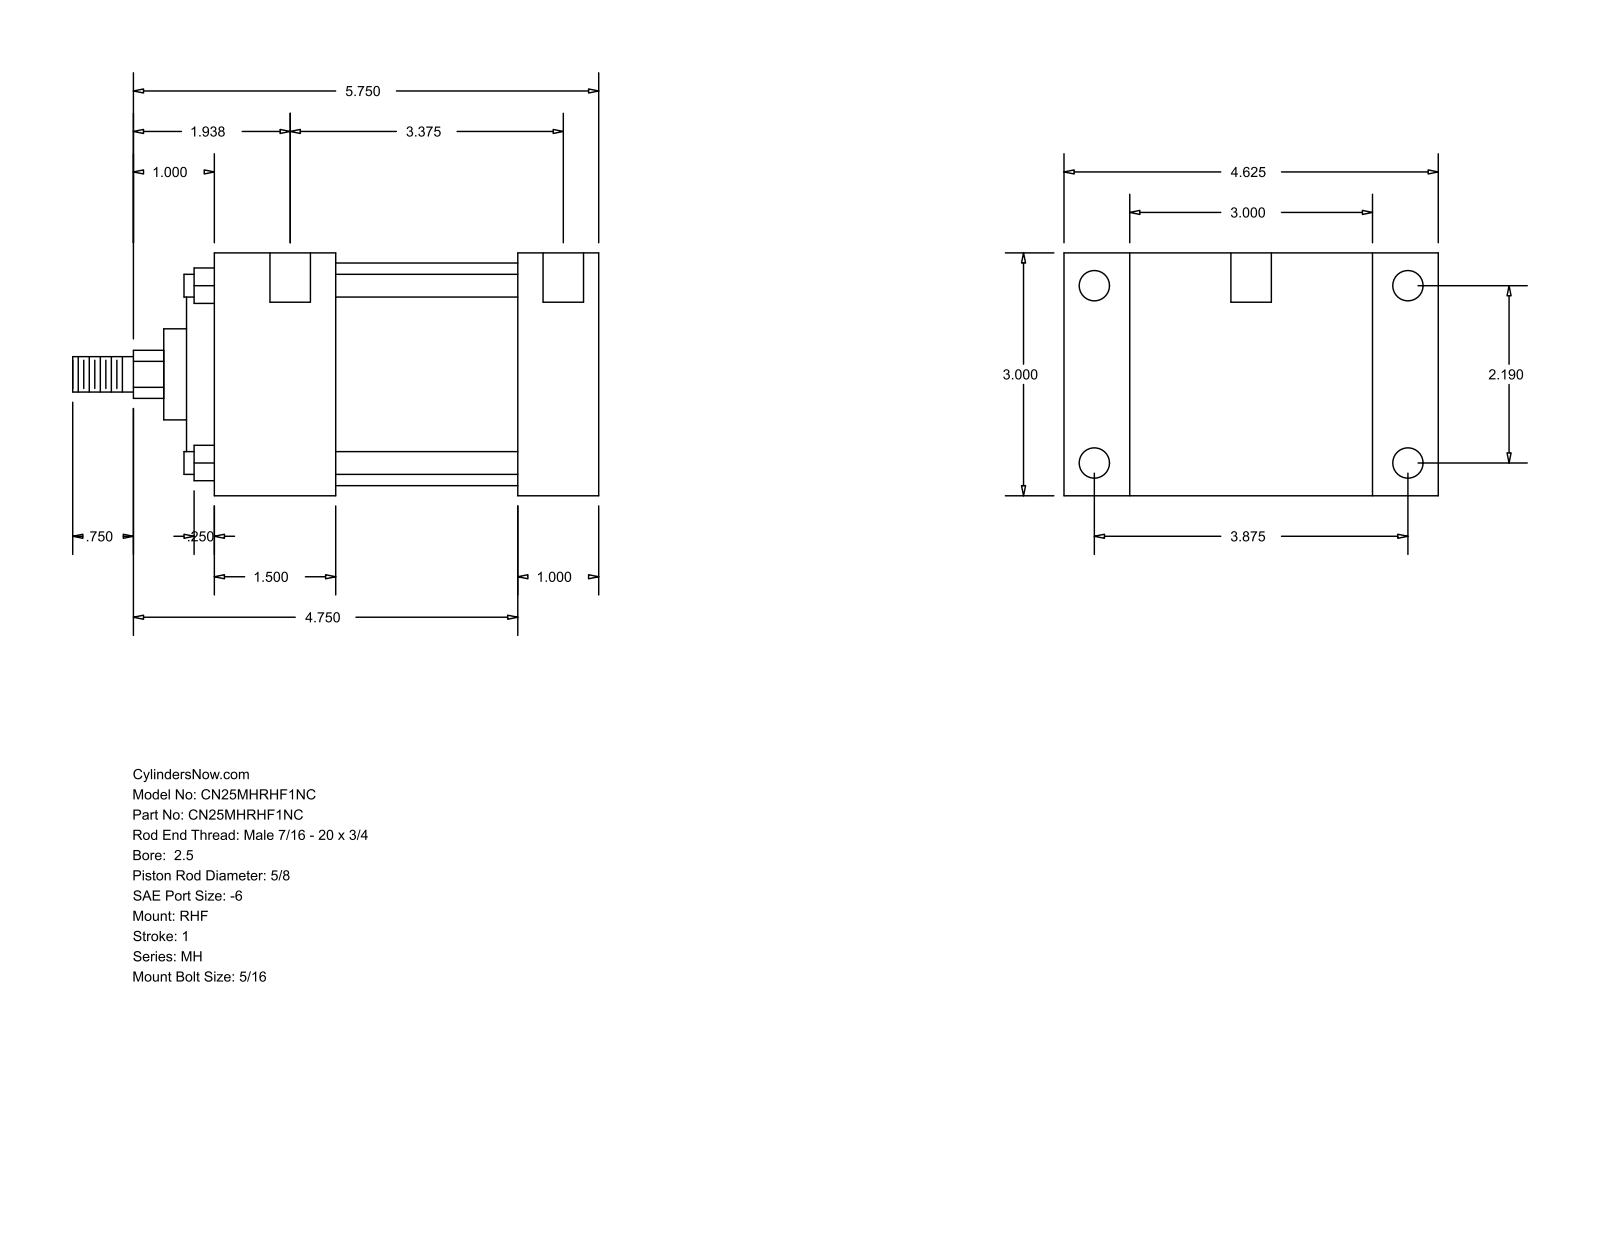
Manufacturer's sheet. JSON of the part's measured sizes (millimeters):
{"part_name": "MH_RHF__0250_0.625", "step_written_by": "GSSL Pune (CONFIG_CONTROL_DESIGN)", "units": "millimeters", "bodies": {"solids": 0, "faces": 90, "planar": 61, "cylindrical": 29, "other": 0}, "overall_size": [165.1, 117.47, 76.2], "round_holes": [[5.56, 4], [9.53, 4], [12.7, 2]], "round_bosses_or_shafts": [[7.14, 4], [69.85, 1], [55.55, 1], [28.57, 1], [15.88, 1], [11.11, 1]], "partial_cylinders_radius": [[7.54, 1]], "face_to_face_distances": [76.2, 25.4, 20.64, 96.84, 120.65, 95.25, 38.1, 82.55, 117.48, 57.15], "hole_center_spacings": [55.62, 93.66, 98.42, 113.05, 3.17, 4.76, 85.73, 88.9]}
